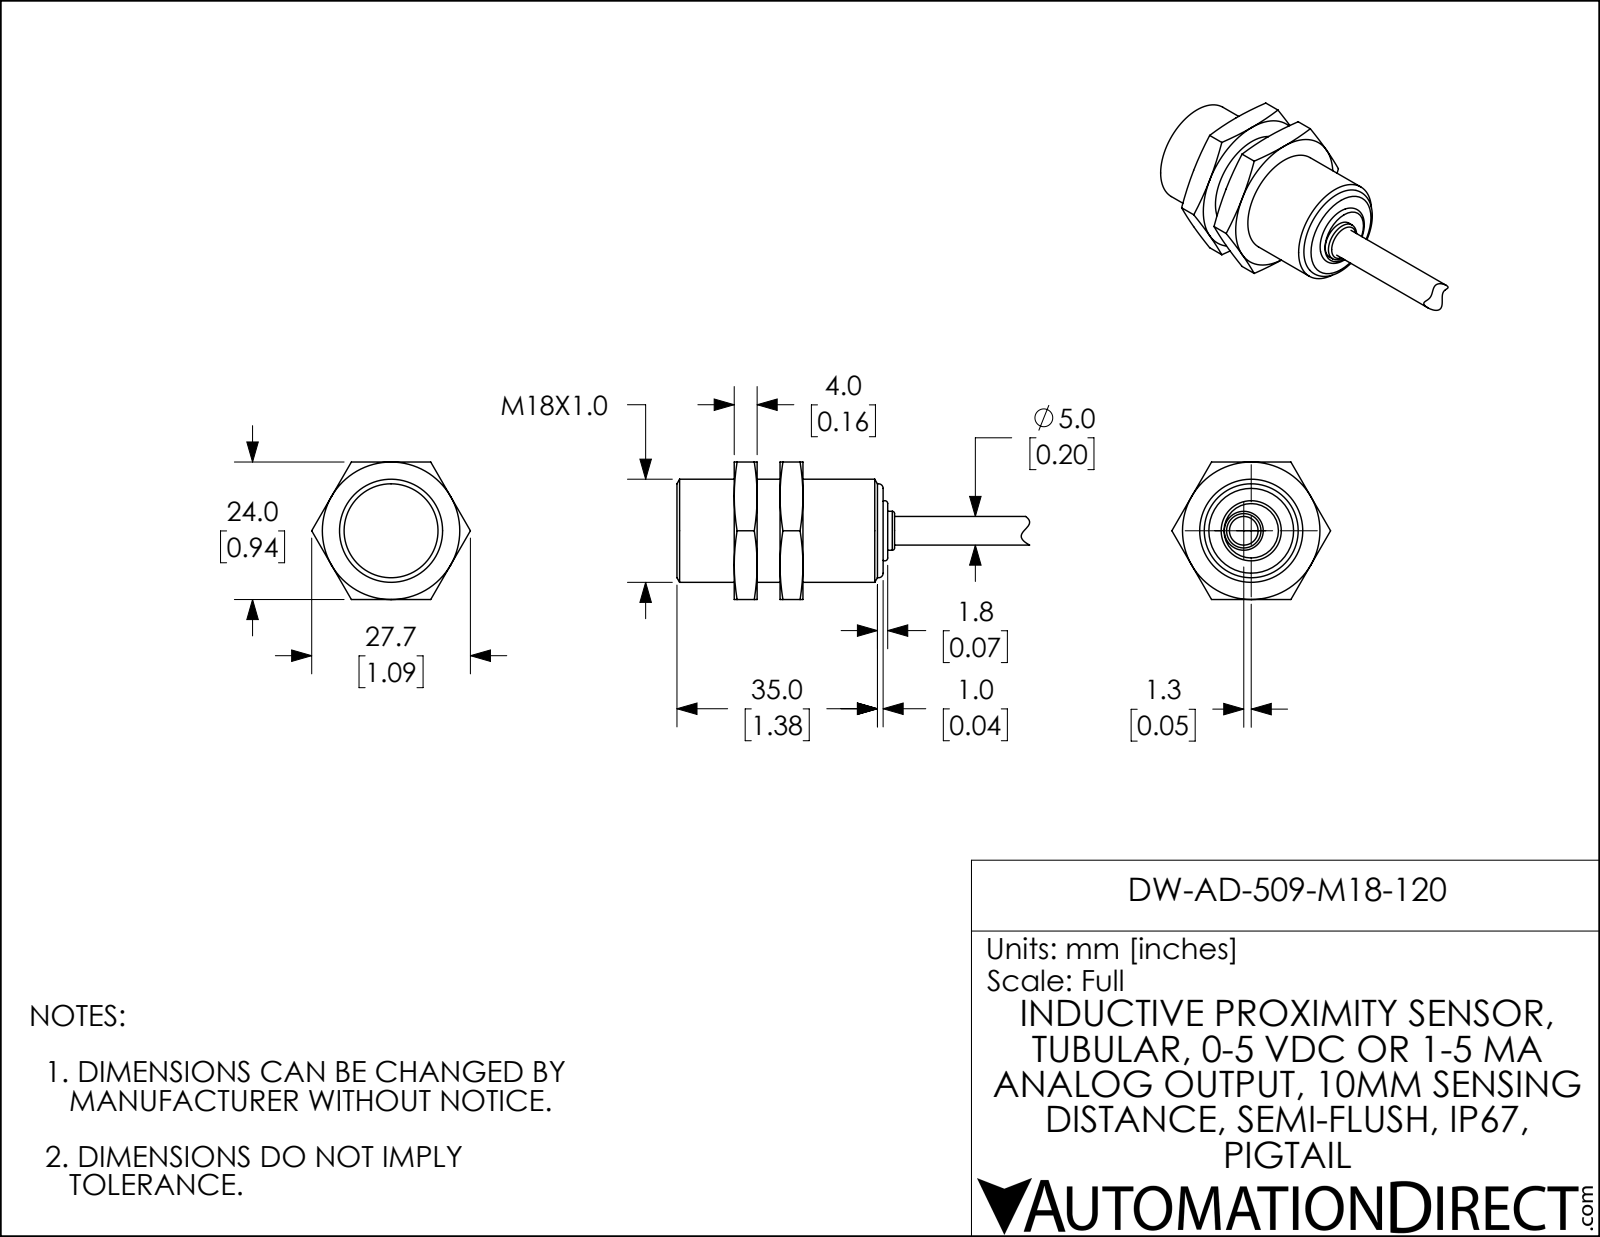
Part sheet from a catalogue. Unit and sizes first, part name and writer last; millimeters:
Units: millimetres
Overall size (bounding box): 61.6 × 18 × 18
Round bosses / shafts (diameter × count): ⌀18 ×1, ⌀6.8 ×1, ⌀5 ×1
Main face-to-face distances: 36, 36.8, 0.8, 38, 2, 1.2, 33, 3, 3.8, 5
Volume: 9 747 mm³ · Surface area: 3 012 mm²
Bodies: 2 solids, 14 faces (5 planar, 3 cylindrical, 6 other)
Part name (STEP PRODUCT): DW-AD-509-M18-x20
STEP written by: SolidWorks 2018 (AUTOMOTIVE_DESIGN)
